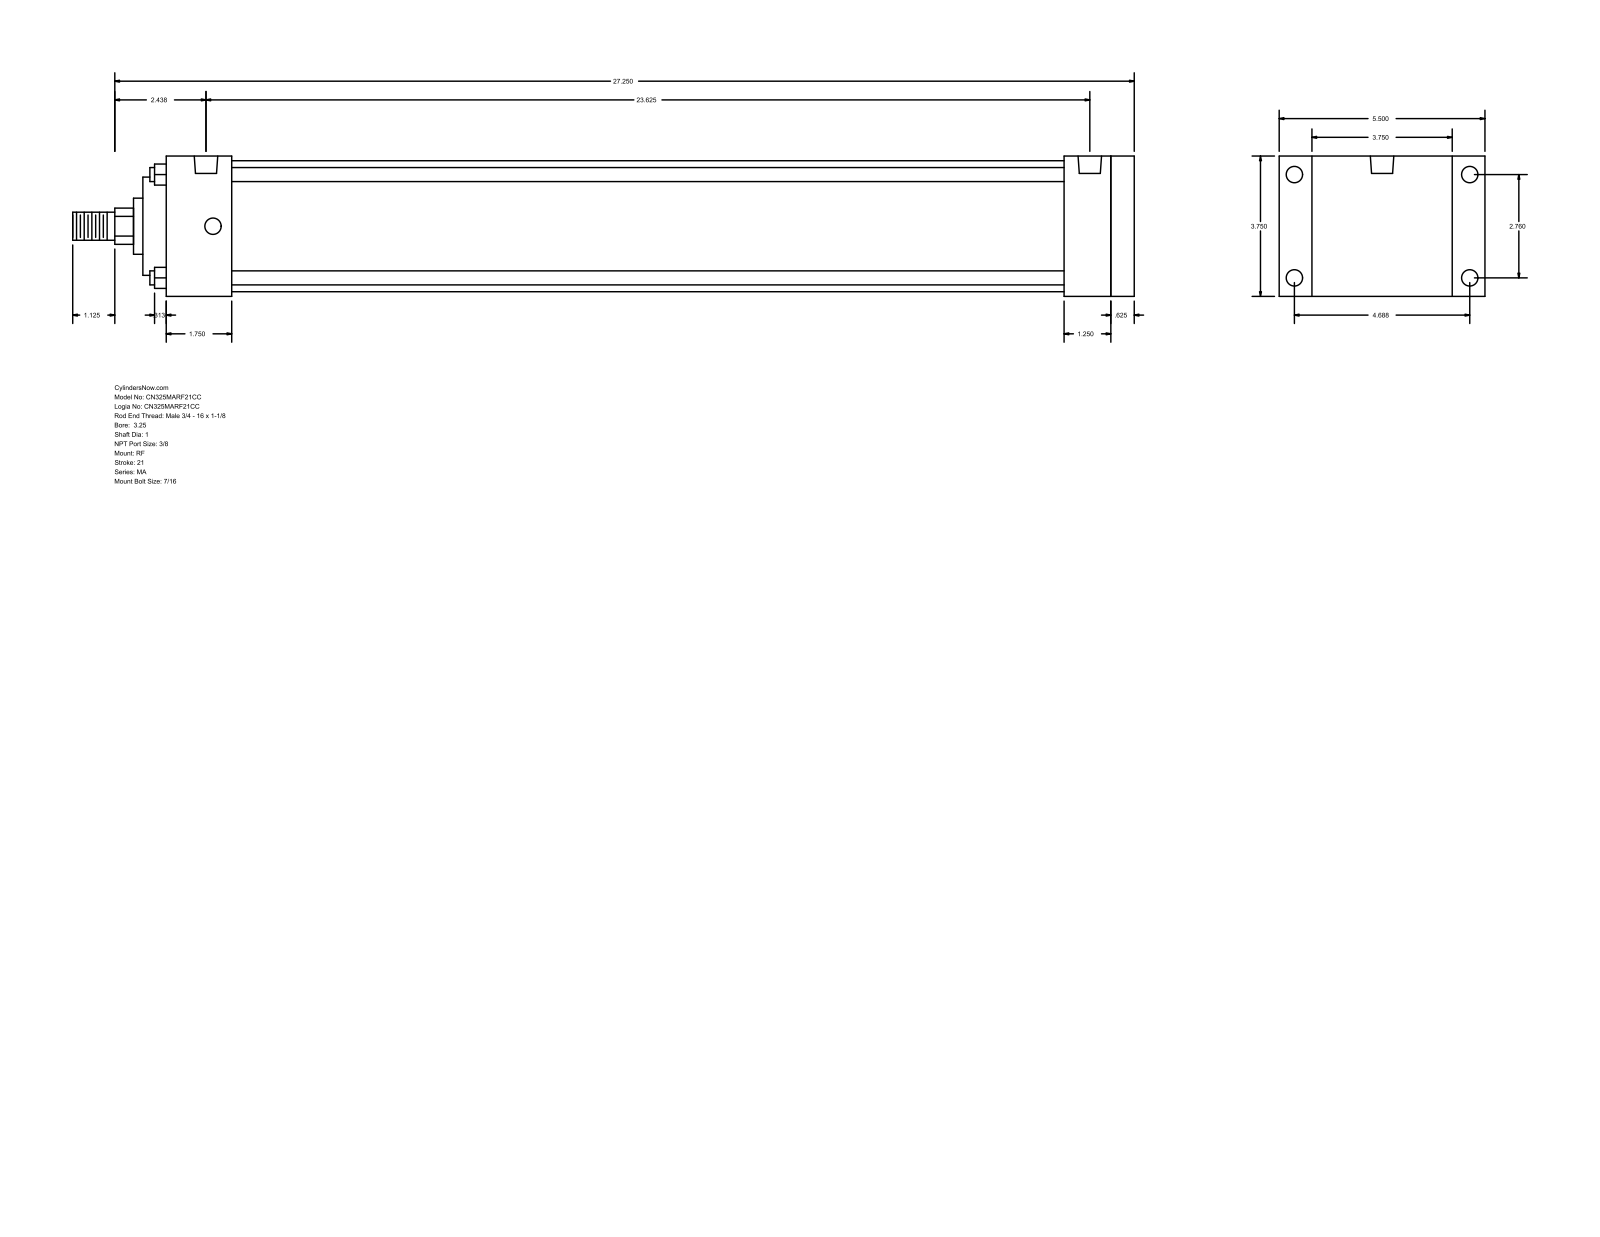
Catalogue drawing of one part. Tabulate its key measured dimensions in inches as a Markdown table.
| quantity | value |
| --- | --- |
| part name | MA_RF__0325_1 |
| STEP written by | GSSL Pune (CONFIG_CONTROL_DESIGN) |
| units | inches |
| bodies | 0 solids, 94 faces (65 planar, 29 cylindrical, 0 other) |
| overall size | 28.375 × 5.5 × 3.75 |
| round holes (diameter × count) | 0.437 × 8, 0.627 × 2 |
| round bosses / shafts (diameter × count) | 0.375 × 4, 3.5 × 1, 2.625 × 1, 1.5 × 1, 1 × 1, 0.75 × 1 |
| partial cylindrical surfaces (radius × count) | 0.484 × 1 |
| main face-to-face distances | 3.75, 25.875, 25.25, 0.625, 0.875, 4.625, 24, 1.25, 1.875, 1.75 |
| hole center spacings | 0.187, 2.76, 4.687, 5.439, 23.25, 23.438, 23.625 |
